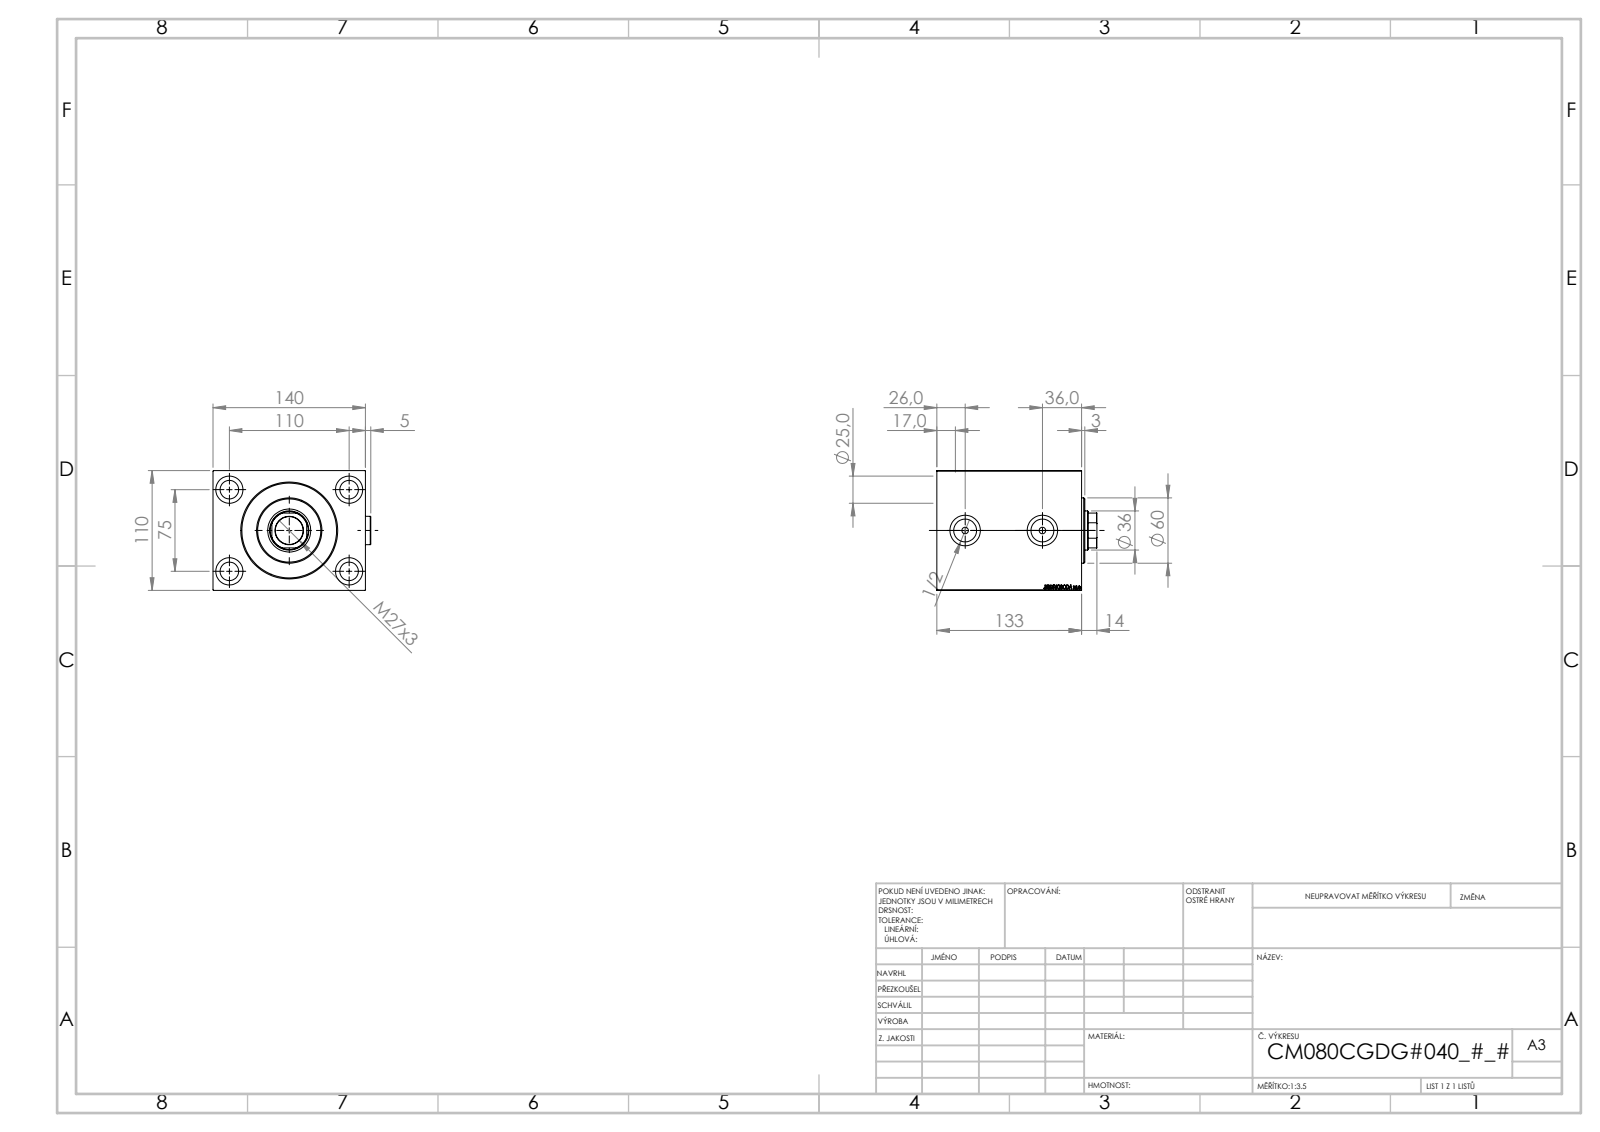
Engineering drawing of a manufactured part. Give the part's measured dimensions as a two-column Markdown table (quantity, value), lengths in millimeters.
| quantity | value |
| --- | --- |
| part name | V450CM_C_Body; Zatka_OIL_PORT; V450CM_C_VCP; V450CM_VC_B |
| STEP written by | SolidWorks 2019 (CONFIG_CONTROL_DESIGN) |
| units | millimeters |
| bodies | 5 solids, 919 faces (443 planar, 78 cylindrical, 398 other) |
| overall size | 147 × 144.9 × 110 |
| volume | 1 716 000 mm³ |
| surface area | 213 843 mm² |
| round holes (diameter × count) | 17 × 4, 25 × 4, 6 × 2, 20.96 × 2, 28 × 2, 25.5 × 1, 36 × 1, 39.5 × 1, 80 × 1, 82 × 1, 87 × 1 |
| round bosses / shafts (diameter × count) | 26 × 2, 60 × 1 |
| partial cylindrical surfaces (radius × count) | 17.5 × 1 |
| main face-to-face distances | 110, 140, 133, 112, 21, 119, 14, 98, 54, 40 |
| hole center spacings | 66.57, 75, 110, 133.14, 71 |
